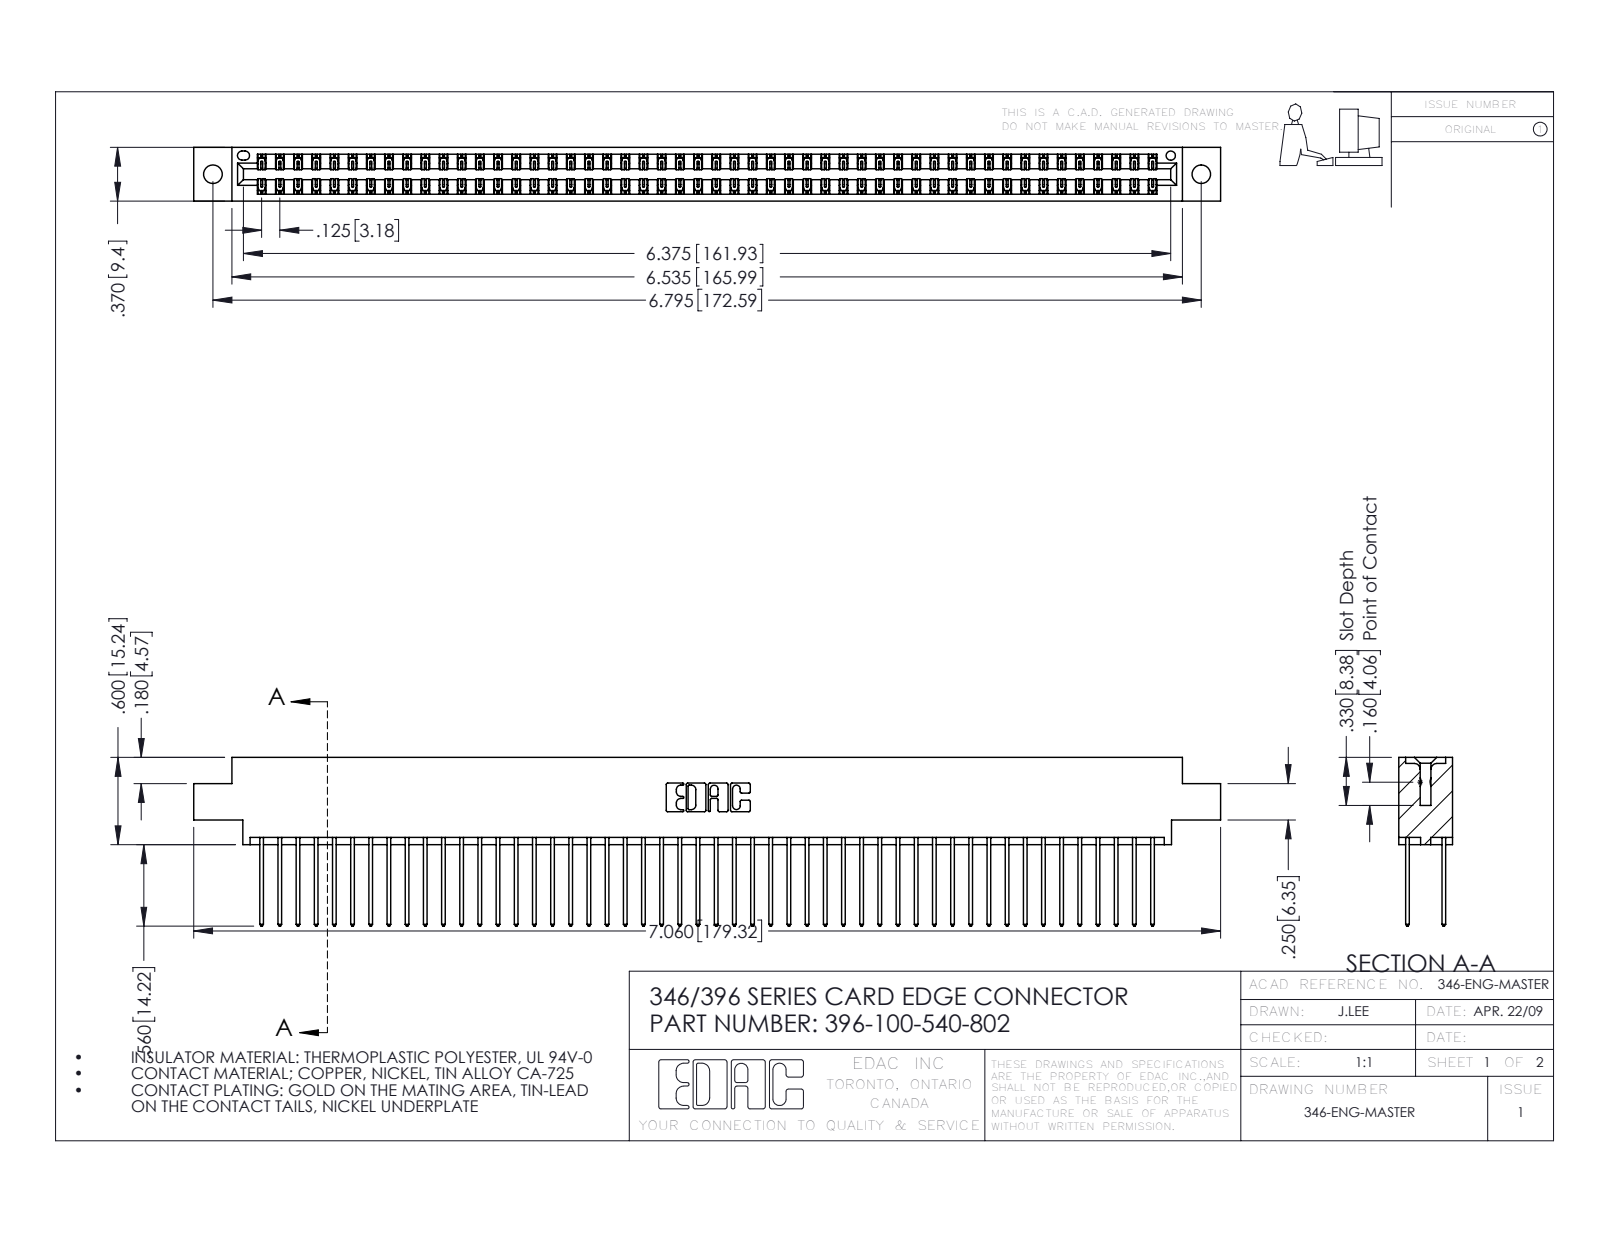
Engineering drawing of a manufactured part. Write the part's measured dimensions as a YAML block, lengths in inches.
part_name: "346 Part_0.170 Offset - 0.128 Dia; 396-100-540-802; 345-292-001_345-293-140"
step_written_by: "SolidWorks 2016 (CONFIG_CONTROL_DESIGN)"
units: inches
bodies: {solids: 101, faces: 5326, planar: 3580, cylindrical: 1746, other: 0}
overall_size: [7.06, 1.16, 0.37]
volume: 1.082
surface_area: 40.62
round_holes:
  - {diameter: 0.128, count: 2}
  - {diameter: 0.064, count: 1}
partial_cylinders:
  - {radius: 0.006, count: 150}
  - {radius: 0.01, count: 100}
  - {radius: 0.01, count: 22}
  - {radius: 0.007, count: 6}
  - {radius: 0.031, count: 6}
  - {radius: 0.026, count: 3}
  - {radius: 0.014, count: 2}
  - {radius: 0.022, count: 2}
face_to_face_distances: [0.048, 0.322, 0.25, 0.072, 0.298, 0.025, 0.37, 0.275, 0.148, 0.222]
hole_center_spacings: [0.246, 6.586, 6.795]
